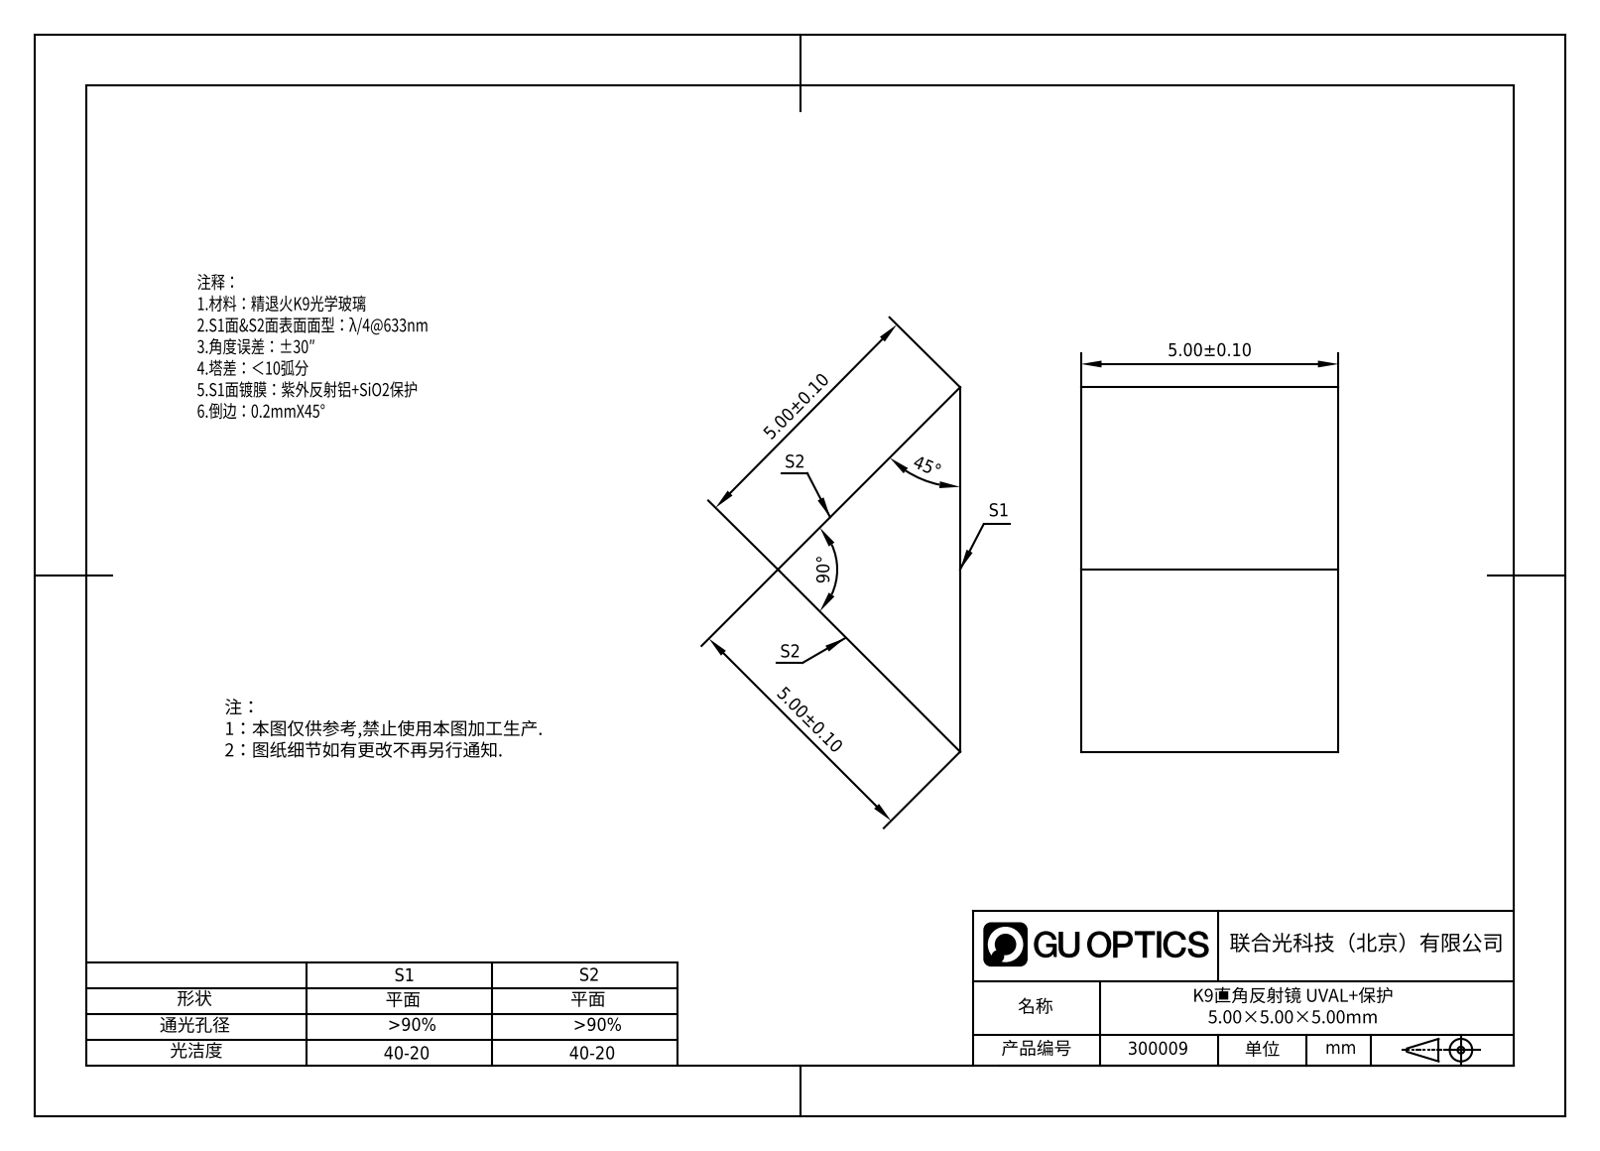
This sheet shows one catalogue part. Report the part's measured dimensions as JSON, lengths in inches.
{"part_name": "300009", "step_written_by": "SolidWorks 2020 (CONFIG_CONTROL_DESIGN)", "units": "inches", "bodies": {"solids": 1, "faces": 5, "planar": 5, "cylindrical": 0, "other": 0}, "overall_size": [0.278, 0.197, 0.139], "volume_in3": 0.004, "surface_area_in2": 0.171, "face_to_face_distances": [0.197]}
